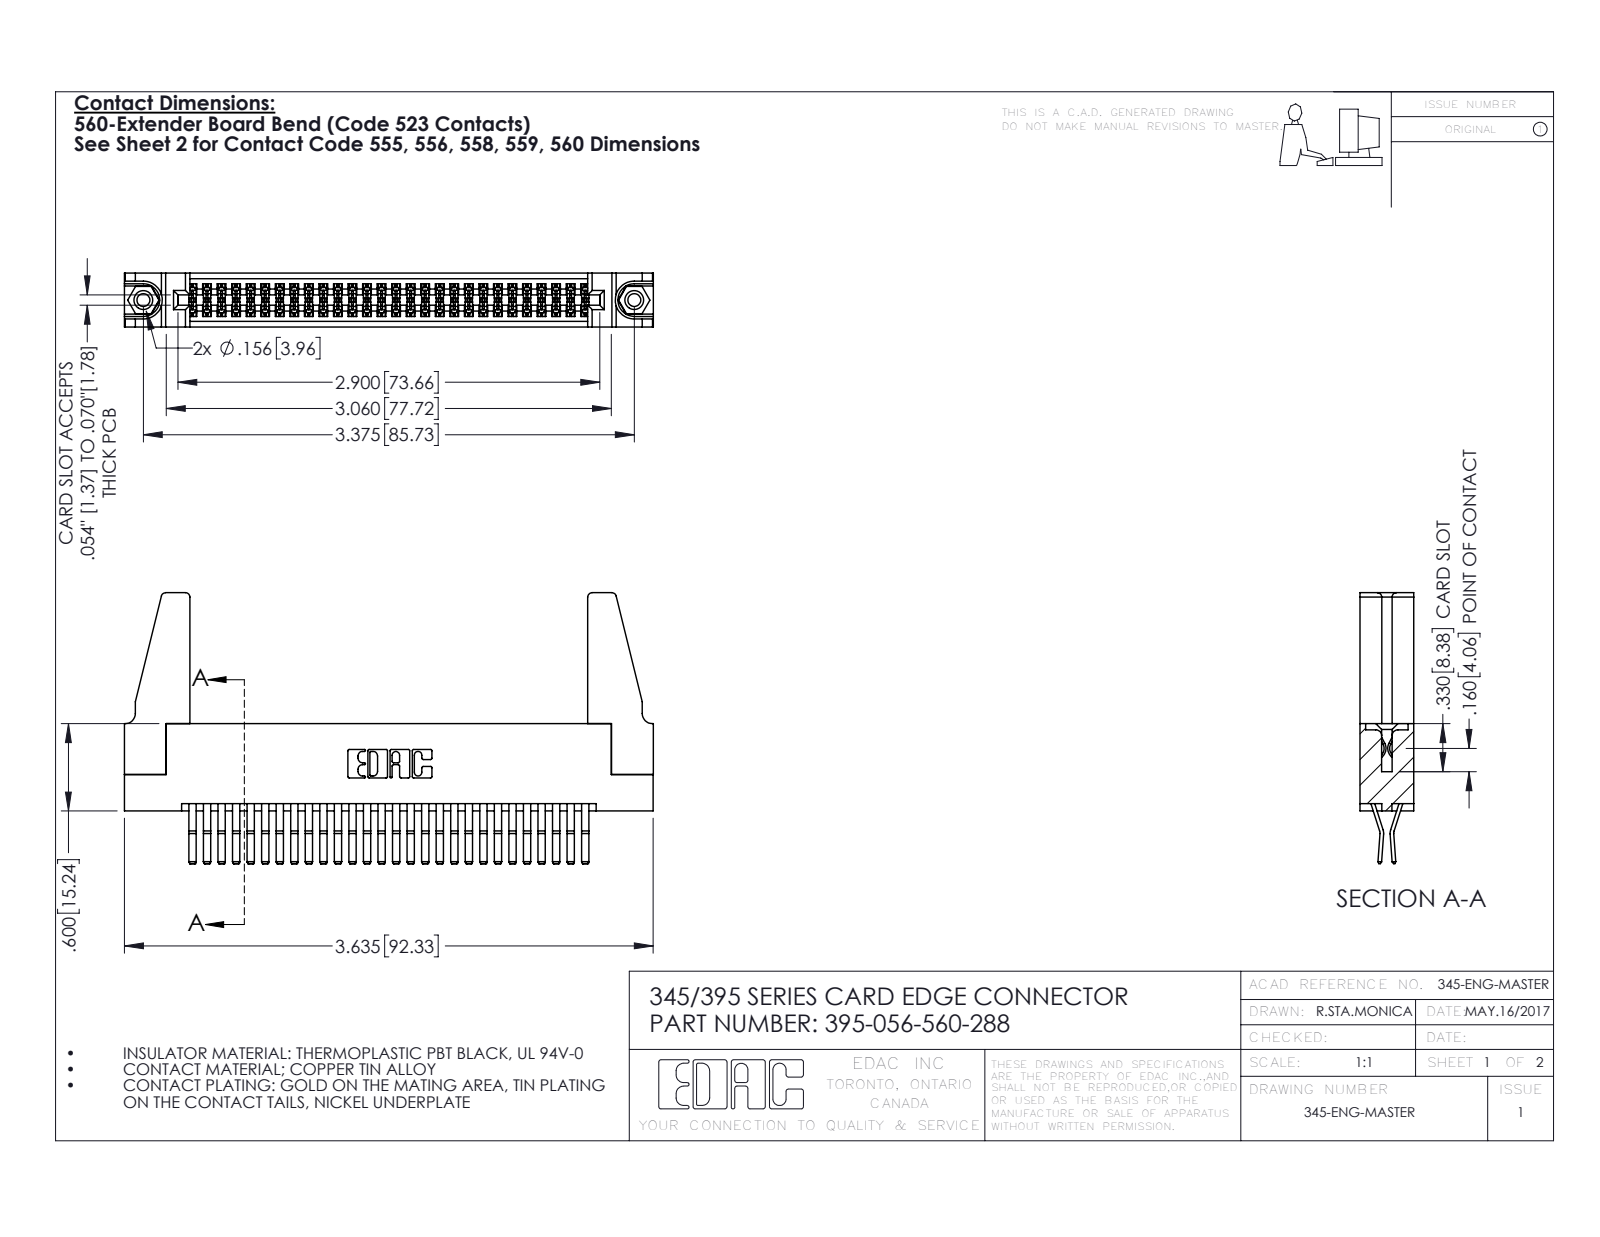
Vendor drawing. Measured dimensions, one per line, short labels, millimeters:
name: 395-056-560-288; 345-220-078_345-220-088; 345 Part_Flush Mounting Lugs - 0.156 Dia-TH; 345-250-001_345-250-001-102 (+1 more)
written by: SolidWorks 2016 (CONFIG_CONTROL_DESIGN)
unit: mm
bodies: 61 solids, 3162 faces (2000 planar, 1146 cylindrical, 16 other)
size: 92.4 × 47.3 × 9.4
volume: 12 500 mm³; area: 17 410 mm²
holes: 2× ⌀2.3, 2× ⌀3.2, 2× ⌀4, 1× ⌀1.6
bosses: 2× ⌀3.9
rounds: 111× R0.2, 22× R0.3, 8× R0.8, 6× R0.2, 6× R0.8, 3× R0.7, 2× R0.3, 2× R0.4
face distances: 1.8, 7.6, 9.4, 0.6, 5.1, 2.5, 6.9, 5.7, 4.4, 3.8
hole spacings: 6.9, 79.8, 85.7
